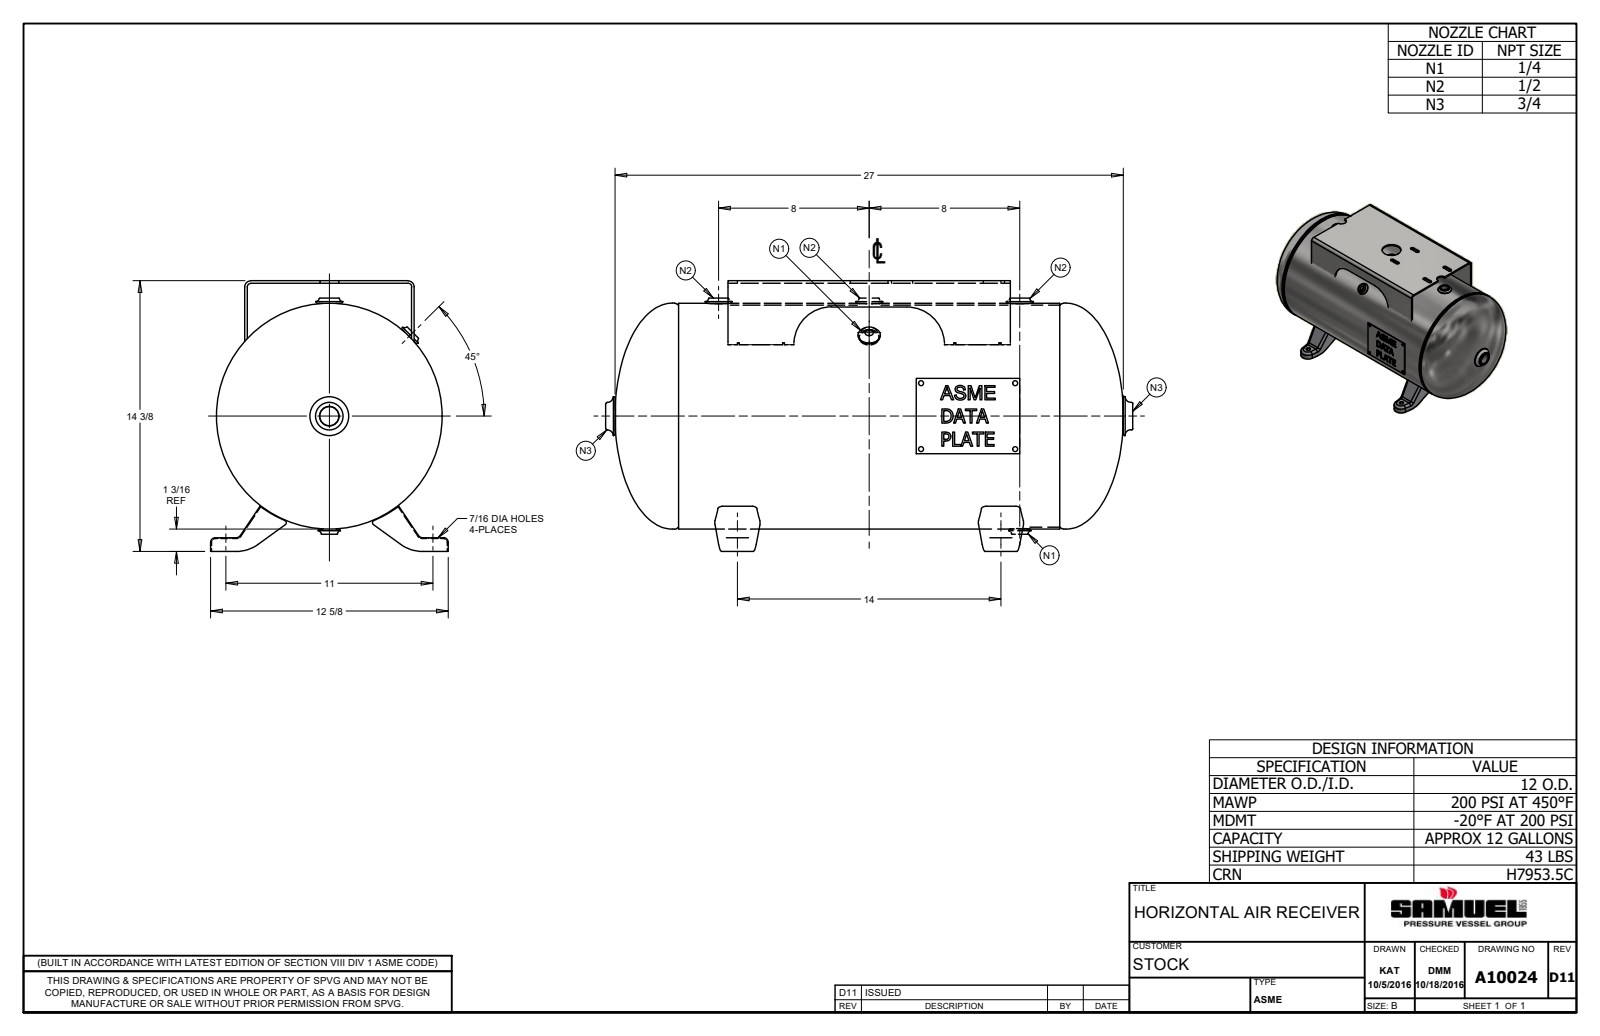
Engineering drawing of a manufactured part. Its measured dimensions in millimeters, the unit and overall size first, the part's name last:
Units: millimetres
Overall size (bounding box): 711.2 × 365.1 × 320.7
Round holes (diameter × count): ⌀6.4 ×4, ⌀11.1 ×4, ⌀18.6 ×3, ⌀31.8 ×3, ⌀11.5 ×2, ⌀27 ×2, ⌀36.5 ×1, ⌀50.8 ×1, ⌀294.4 ×1, ⌀299.7 ×1
Round bosses / shafts (diameter × count): ⌀27 ×2, ⌀304.8 ×1, ⌀304.3 ×1, ⌀299.5 ×1, ⌀52.4 ×1, ⌀36.9 ×1
Partial cylindrical surfaces — rounded edges, fillets, slot ends (radius × count): R6.4 ×18, R5.2 ×16, R4.3 ×8, R17.9 ×4, R19.1 ×4, R50.8 ×4, R3.2 ×2, R4.7 ×2
Main face-to-face distances: 3.4, 3.4, 225.2, 1.2, 228.6, 221.8, 352.4, 266.4, 263, 41.3
Hole centre spacings: 142, 226.1, 405.8, 88.9, 127, 155, 203.2, 279.4
Volume: 2 284 000 mm³ · Surface area: 1 837 000 mm²
Bodies: 16 solids, 514 faces (277 planar, 124 cylindrical, 113 other)
Part name (STEP PRODUCT): A10024; A10024-1; A10024-2; H12094J (+8 more)
STEP written by: Autodesk Inventor 2019 (CONFIG_CONTROL_DESIGN)
